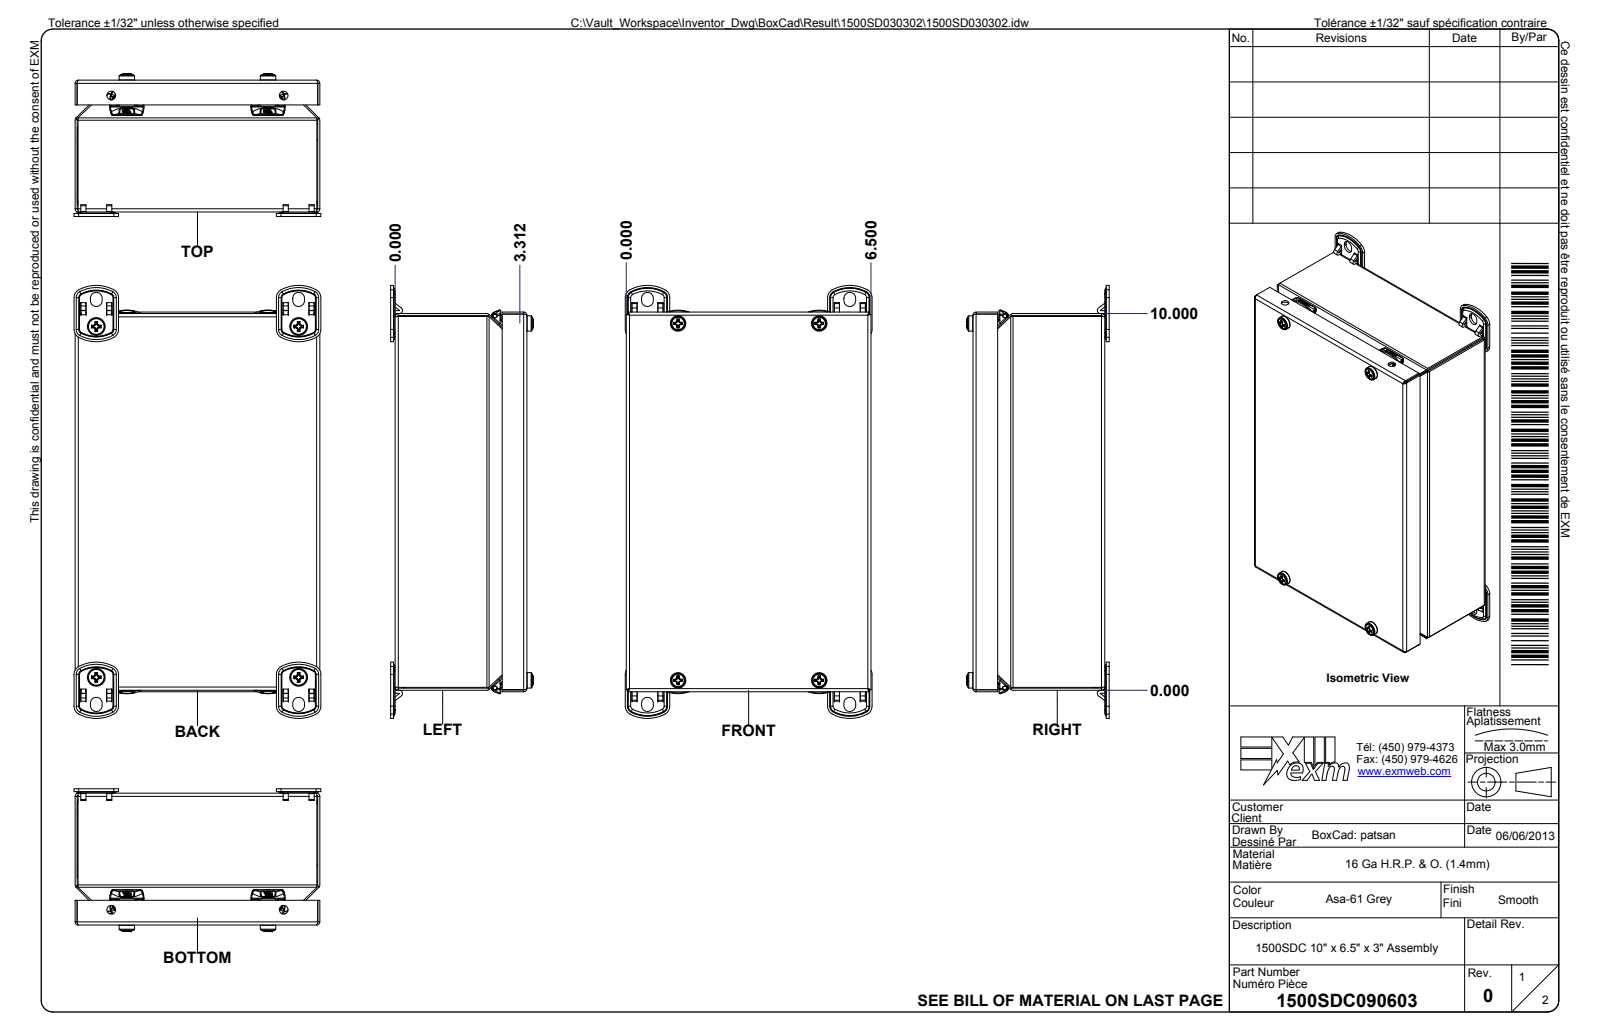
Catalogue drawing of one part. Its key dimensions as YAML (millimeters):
part_name: "1412SDC090603; 1412SDC090603B; 1412SDC090603B-P; RIVET_NUT_M5_FH_OE (+8 more)"
step_written_by: "Autodesk Inventor 2024 (AUTOMOTIVE_DESIGN)"
units: millimeters
bodies: {solids: 29, faces: 2870, planar: 740, cylindrical: 994, other: 1136}
overall_size: [292, 171.1, 87.4]
volume: 261200
surface_area: 373500
round_holes:
  - {diameter: 4, count: 4}
  - {diameter: 5, count: 4}
  - {diameter: 5, count: 4}
  - {diameter: 7, count: 4}
  - {diameter: 0.8, count: 2}
  - {diameter: 5.1, count: 2}
  - {diameter: 5.8, count: 2}
  - {diameter: 6.1, count: 2}
round_bosses_or_shafts:
  - {diameter: 15, count: 4}
  - {diameter: 12.7, count: 4}
  - {diameter: 7, count: 4}
  - {diameter: 5.9, count: 4}
  - {diameter: 4.9, count: 4}
  - {diameter: 3.5, count: 4}
  - {diameter: 10, count: 2}
  - {diameter: 0.9, count: 2}
partial_cylinders:
  - {radius: 0.2, count: 224}
  - {radius: 0.1, count: 82}
  - {radius: 0.3, count: 48}
  - {radius: 0.3, count: 32}
  - {radius: 0.8, count: 28}
  - {radius: 1, count: 28}
  - {radius: 2.1, count: 24}
  - {radius: 6, count: 24}
face_to_face_distances: [1.3, 78.5, 79.9, 1.3, 77.2, 78.5, 163.8, 252.7, 3, 165.1]
hole_center_spacings: [148.5, 155.8, 27.9, 210.5, 256.1, 22.3, 27.9, 134.5]
